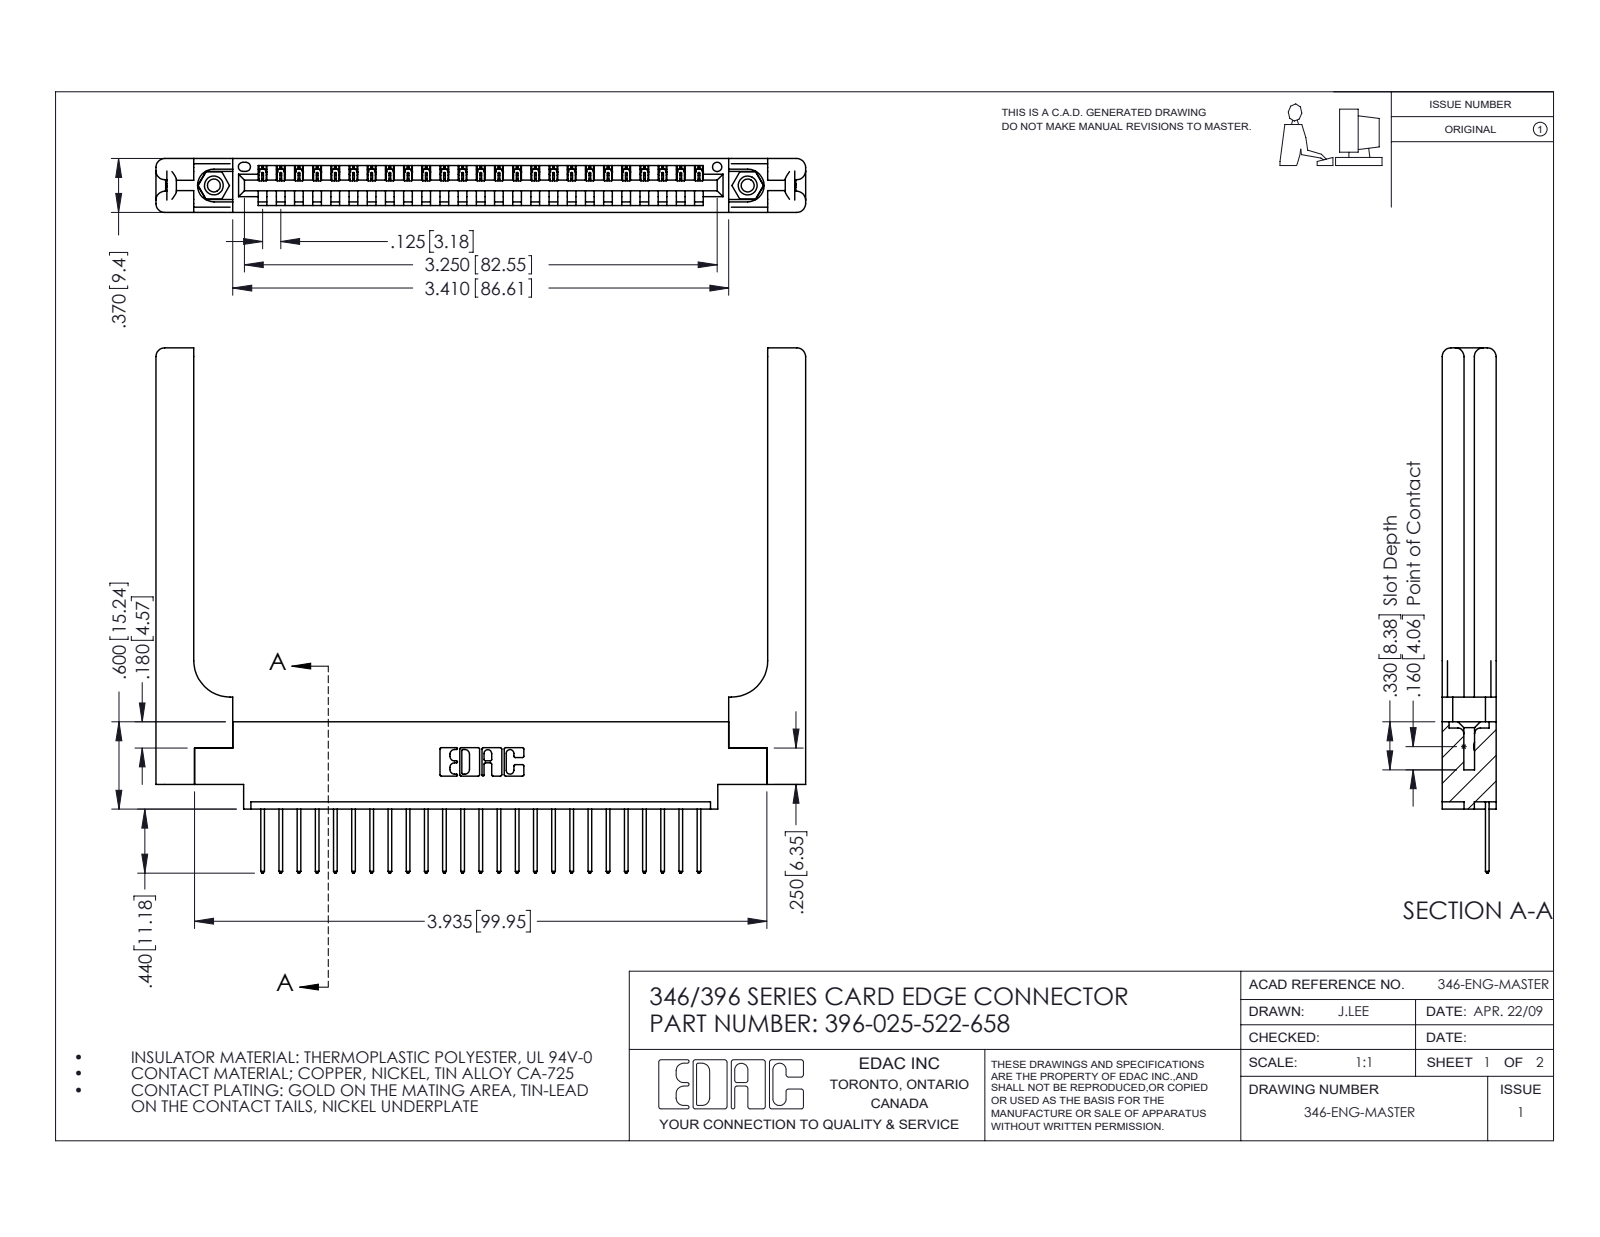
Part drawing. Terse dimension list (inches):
name: 346-220-058_345-220-058; 346 Part_0.170 Offset - 0.156 Dia-TH; 396-025-522-658; 345-250-001_345-250-001-102 (+1 more)
written by: SolidWorks 2016 (CONFIG_CONTROL_DESIGN)
unit: in
bodies: 30 solids, 1832 faces (1228 planar, 544 cylindrical, 60 other)
size: 4.466 × 3.61 × 0.37
volume: 1.105 in³; area: 28.64 in²
holes: 2× ⌀0.089, 2× ⌀0.125, 2× ⌀0.156, 1× ⌀0.064
bosses: 2× ⌀0.155
rounds: 50× R0.006, 50× R0.01, 22× R0.01, 16× R0.06, 6× R0.007, 6× R0.031, 3× R0.026, 2× R0.03
face distances: 0.37, 0.072, 0.048, 0.322, 0.15, 0.148, 0.25, 0.298, 0.025, 0.077
hole spacings: 0.246, 3.462, 3.67
